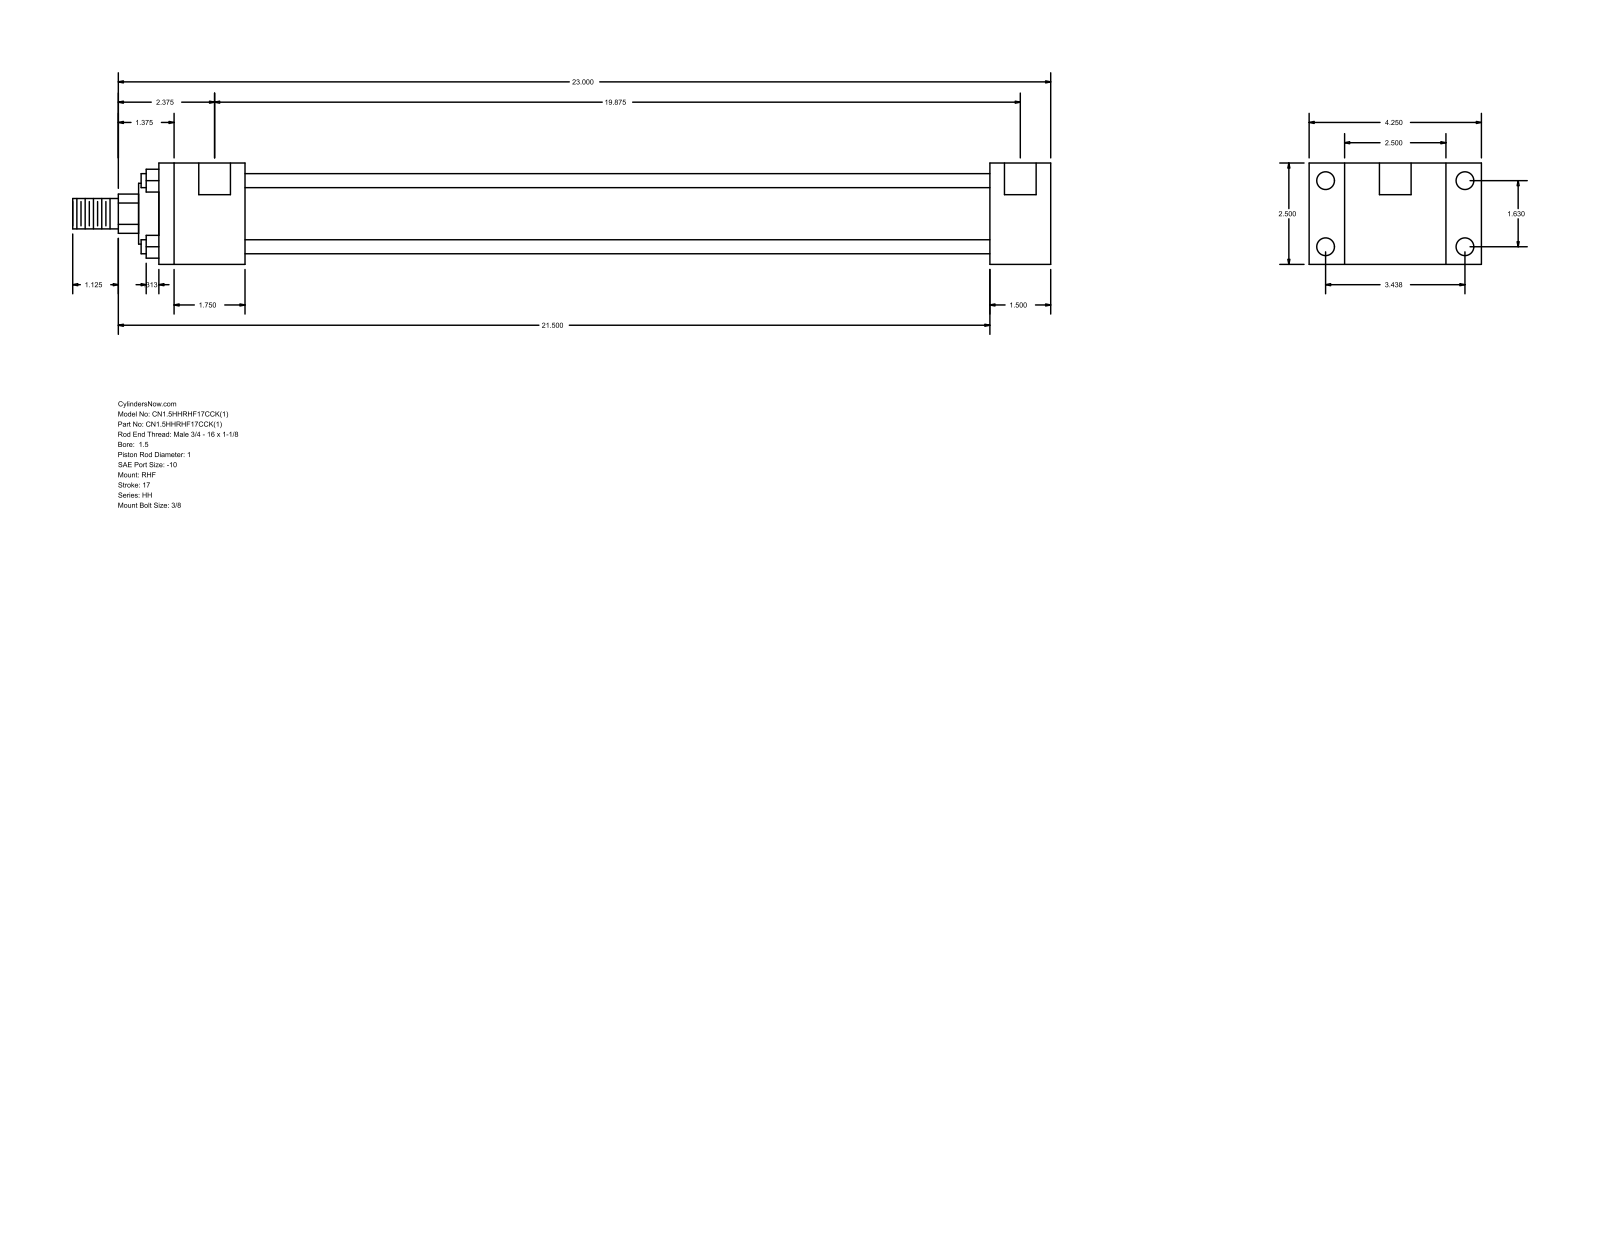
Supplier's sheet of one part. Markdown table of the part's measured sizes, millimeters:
| quantity | value |
| --- | --- |
| part name | HH_RHF__0150_1 |
| STEP written by | GSSL Pune (CONFIG_CONTROL_DESIGN) |
| units | millimeters |
| bodies | 0 solids, 88 faces (60 planar, 28 cylindrical, 0 other) |
| overall size | 612.77 × 107.95 × 63.5 |
| round holes (diameter × count) | 5.56 × 4, 11.13 × 4, 19.84 × 2 |
| round bosses / shafts (diameter × count) | 8.76 × 4, 44.45 × 1, 38.1 × 1, 25.4 × 1, 19.05 × 1 |
| partial cylindrical surfaces (radius × count) | 12.29 × 1 |
| main face-to-face distances | 63.5, 22.23, 85.73, 38.1, 107.96, 466.72, 504.82, 53.98, 520.7, 558.8 |
| hole center spacings | 1.59, 41.4, 87.32, 96.64, 506.41, 508, 504.82 |
